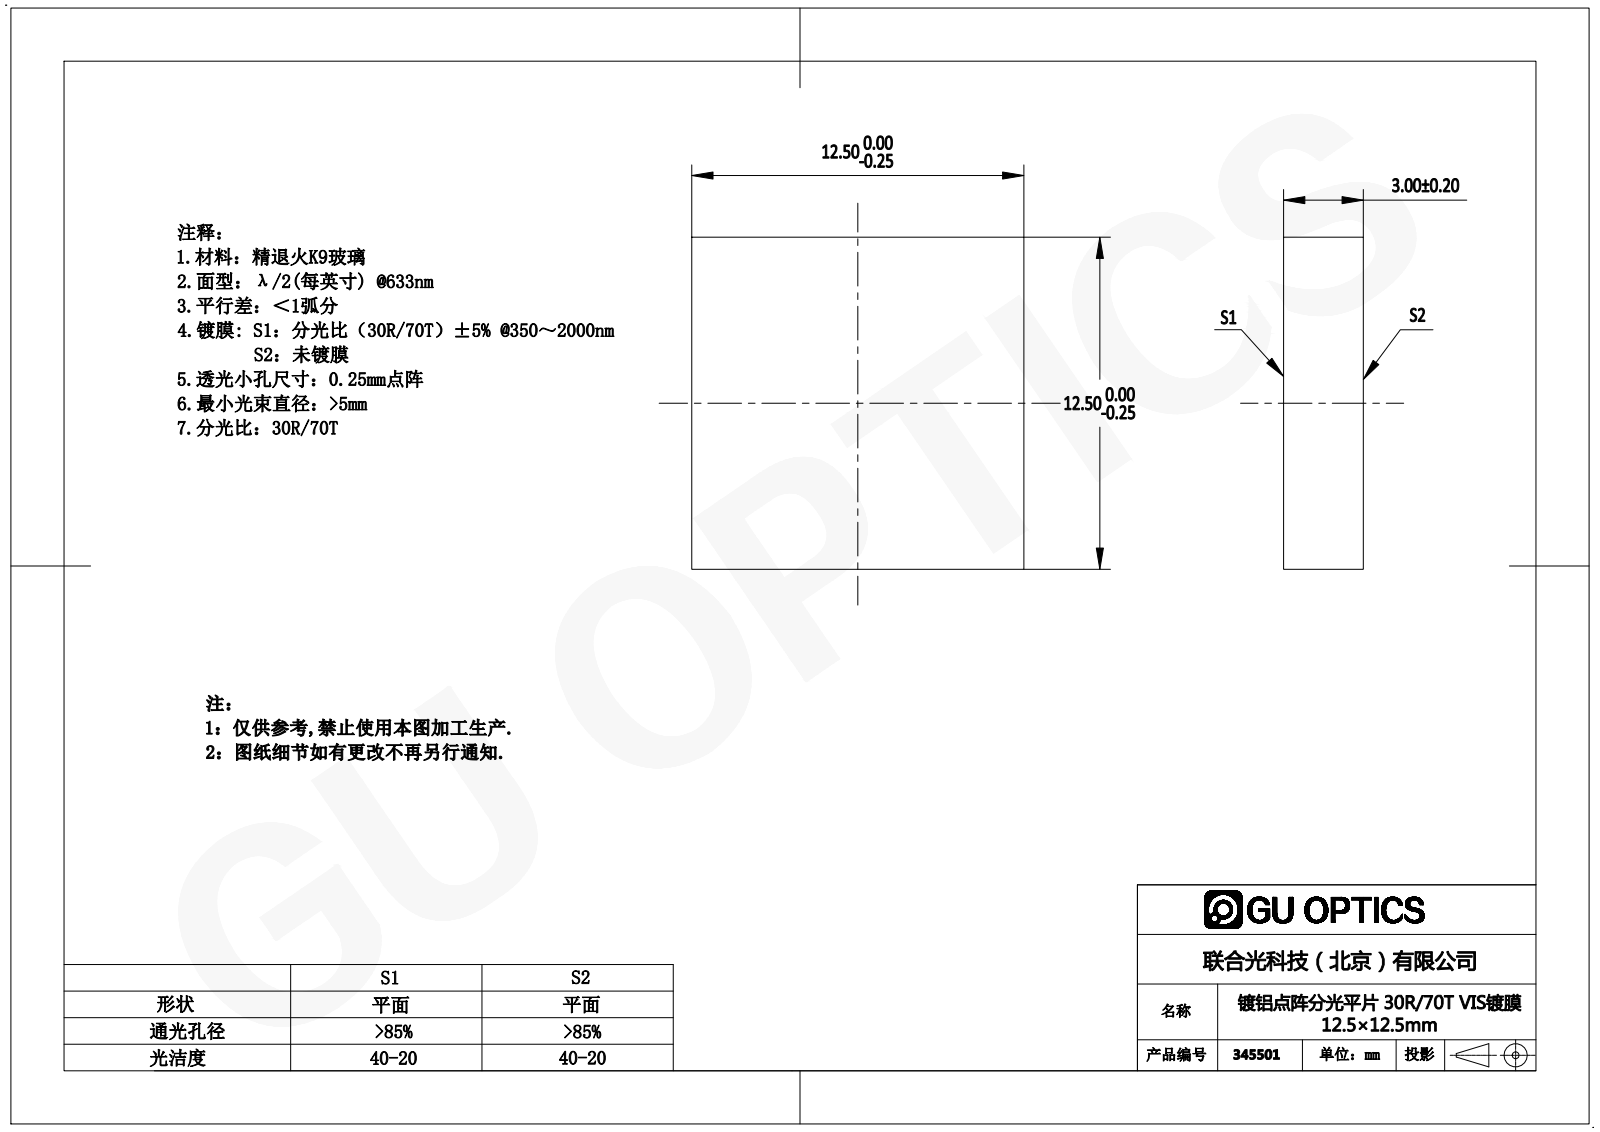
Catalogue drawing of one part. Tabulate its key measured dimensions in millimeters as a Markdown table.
| quantity | value |
| --- | --- |
| part name | 345501 |
| STEP written by | SolidWorks 2016 (AUTOMOTIVE_DESIGN) |
| units | millimeters |
| bodies | 1 solid, 6 faces (6 planar, 0 cylindrical, 0 other) |
| overall size | 12.5 × 12.5 × 3 |
| volume | 469 mm³ |
| surface area | 462 mm² |
| main face-to-face distances | 3, 12.5 |
